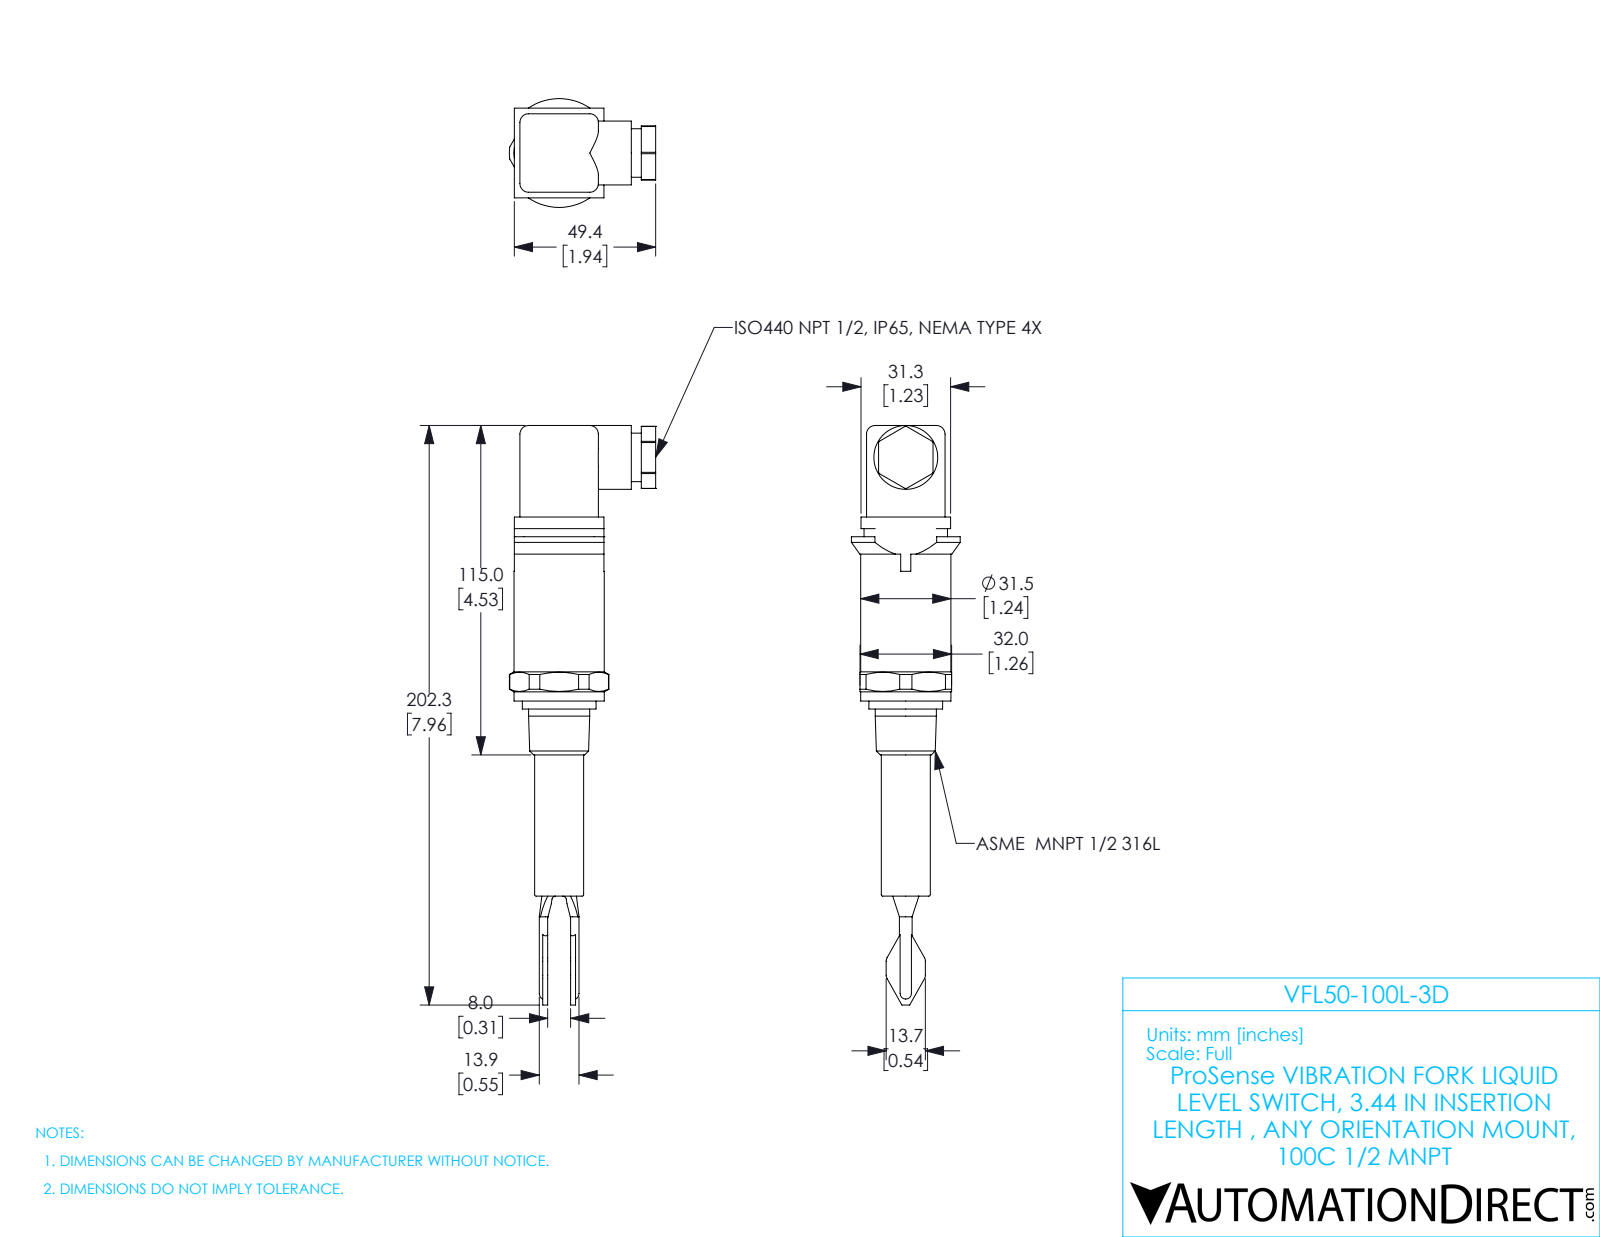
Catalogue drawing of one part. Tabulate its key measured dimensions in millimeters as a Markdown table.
| quantity | value |
| --- | --- |
| part name | VFL50-100L-3D |
| STEP written by | SolidWorks 2017 (AUTOMOTIVE_DESIGN) |
| units | millimeters |
| bodies | 1 solid, 158 faces (79 planar, 58 cylindrical, 21 other) |
| overall size | 202.3 × 51.1 × 38 |
| volume | 103 000 mm³ |
| surface area | 18 960 mm² |
| round bosses / shafts (diameter × count) | 31.5 × 1, 25.8 × 1, 22.3 × 1, 21.3 × 1, 17.1 × 1, 16.9 × 1 |
| partial cylindrical surfaces (radius × count) | 3 × 8, 1.2 × 4, 2.4 × 4, 3.9 × 4, 2.2 × 2, 10.8 × 1, 17.4 × 1, 19 × 1 |
| main face-to-face distances | 27.4, 2, 29.4, 11.7, 19.7, 9.7, 17.7, 31.3, 29.7, 49.4 |
